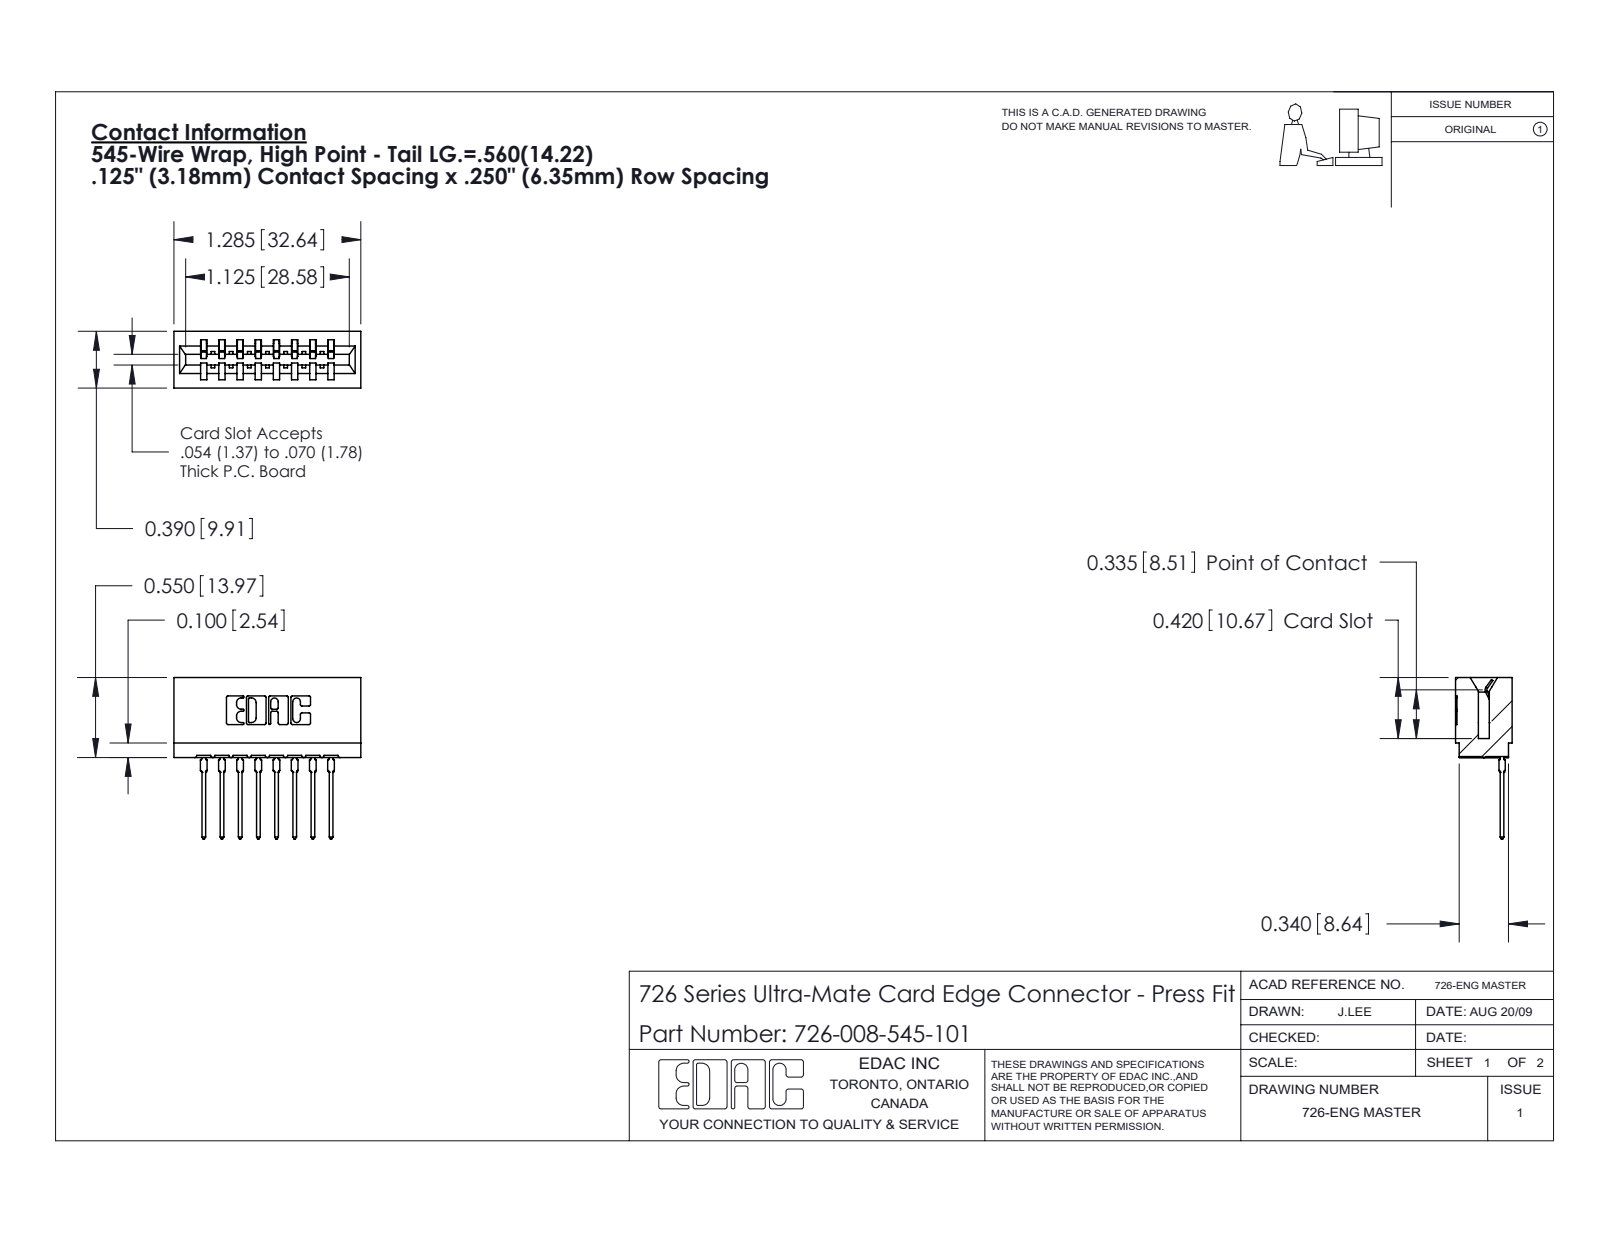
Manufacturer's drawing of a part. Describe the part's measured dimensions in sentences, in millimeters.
The part is named "726-008-545-101; 726 Part_.515 Slot Depth - 01; 746-292-001_545". Its 3-D file was written by "SolidWorks 2020 (CONFIG_CONTROL_DESIGN)". It is 9 solids with 961 faces: 559 planar, 194 cylindrical and 208 other. Overall it measures 32.6 by 28.2 by 9.9 millimeters. Its volume is 3 130 cubic millimeters and its surface area 4 390 square millimeters. Partial cylindrical surfaces (rounded edges, fillets, slot ends): 22 of radius 0.3, 16 of radius 0.5, 9 of radius 0.4, 6 of radius 0.2, 6 of radius 0.8, 4 of radius 0.1, 4 of radius 0.3, 3 of radius 0.7. The main face-to-face distances are 6.4, 1.1, 3.2, 12.7, 8.5, 1.4, 5.3, 3.2, 7.4, 9.5.
